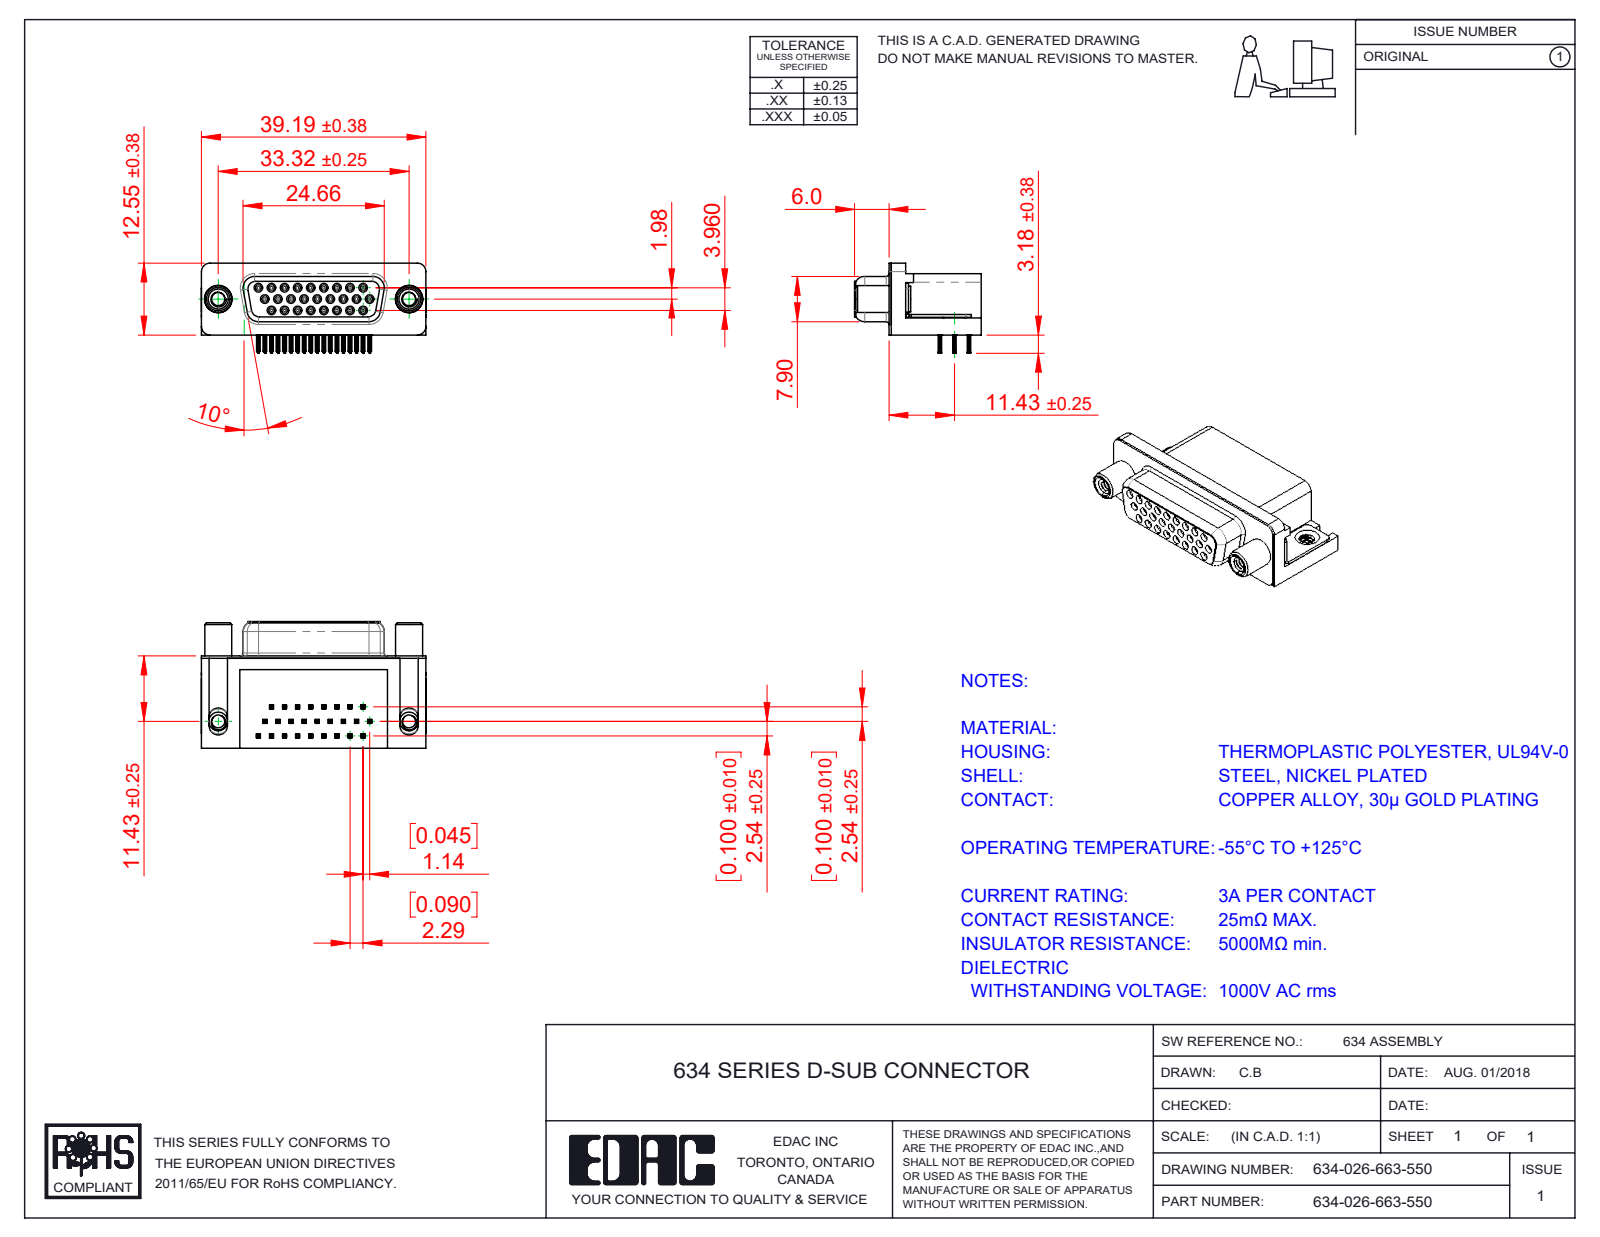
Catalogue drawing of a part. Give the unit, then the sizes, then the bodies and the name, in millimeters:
Units: millimetres
Overall size (bounding box): 39.22 × 22.1 × 16.25
Round holes (diameter × count): ⌀0.8 ×26, ⌀0.9 ×26, ⌀2 ×2, ⌀2.3 ×2, ⌀3.1 ×2, ⌀4 ×2, ⌀4.8 ×2, ⌀5 ×2
Round bosses / shafts (diameter × count): ⌀1.2 ×26, ⌀4.9 ×2, ⌀4.7 ×2, ⌀4.5 ×2, ⌀3.85 ×2, ⌀3 ×2
Partial cylindrical surfaces — rounded edges, fillets, slot ends (radius × count): R0.1 ×208, R0.15 ×104, R0.35 ×52, R0.34 ×26, R1 ×19, R0.28 ×8, R1.35 ×8, R1.5 ×8
Main face-to-face distances: 0.4, 10.34, 0.35, 15.7, 16.1, 6.65, 2.5, 0.85, 2.9, 10.69
Hole centre spacings: 2.29, 4.57, 2.28, 3.96, 6.05, 2.3, 2.27, 4.58
Volume: 6 466 mm³ · Surface area: 9 353 mm²
Bodies: 32 solids, 4095 faces (1805 planar, 952 cylindrical, 1338 other)
Part name (STEP PRODUCT): Round Threaded Standoff; Contact Middle; 634-026-663-550; 634 Housing_26 Socket (+4 more)
STEP written by: SolidWorks 2016 (CONFIG_CONTROL_DESIGN)
